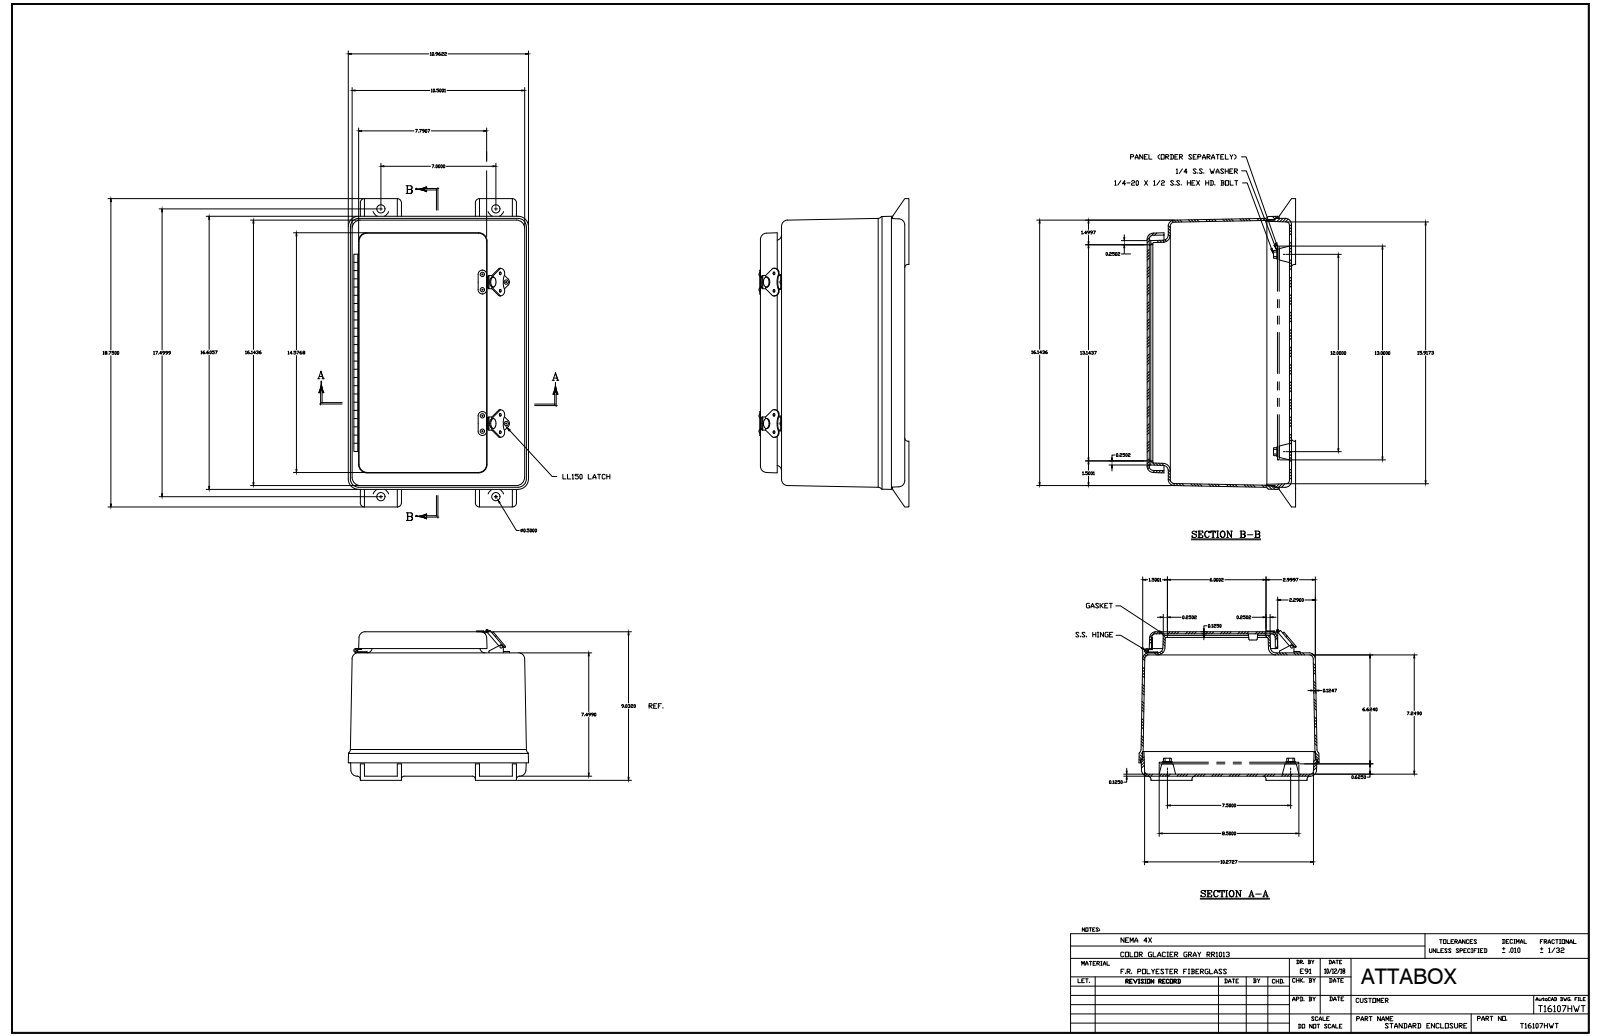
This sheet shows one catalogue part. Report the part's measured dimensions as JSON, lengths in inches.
{"part_name": "T16107HWT", "step_written_by": "SolidWorks 2018 (AUTOMOTIVE_DESIGN)", "units": "inches", "bodies": {"solids": 31, "faces": 1002, "planar": 374, "cylindrical": 378, "other": 250}, "overall_size": [18.75, 10.969, 9.206], "volume_in3": 125.2, "surface_area_in2": 1895, "round_holes": [[0.13, 17], [0.063, 8], [0.065, 5], [0.138, 4], [0.187, 4], [0.4, 4], [0.281, 2], [0.51, 2], [0.51, 2], [0.065, 1], [0.125, 1], [0.135, 1]], "round_bosses_or_shafts": [[0.14, 8], [0.297, 6], [0.5, 2], [0.25, 1], [0.2, 1], [0.135, 1]], "partial_cylinders_radius": [[0.01, 59], [0.25, 28], [0.375, 22], [0.188, 12], [0.5, 12], [0.313, 9], [0.03, 8], [0.1, 5]], "face_to_face_distances": [0.125, 0.125, 8.656, 7.375, 8.781, 8.656, 8.531, 1.281, 7.5, 1.156], "hole_center_spacings": [5.5, 0.937, 8.625, 11, 1.512, 2.404, 2.761, 4.051]}
